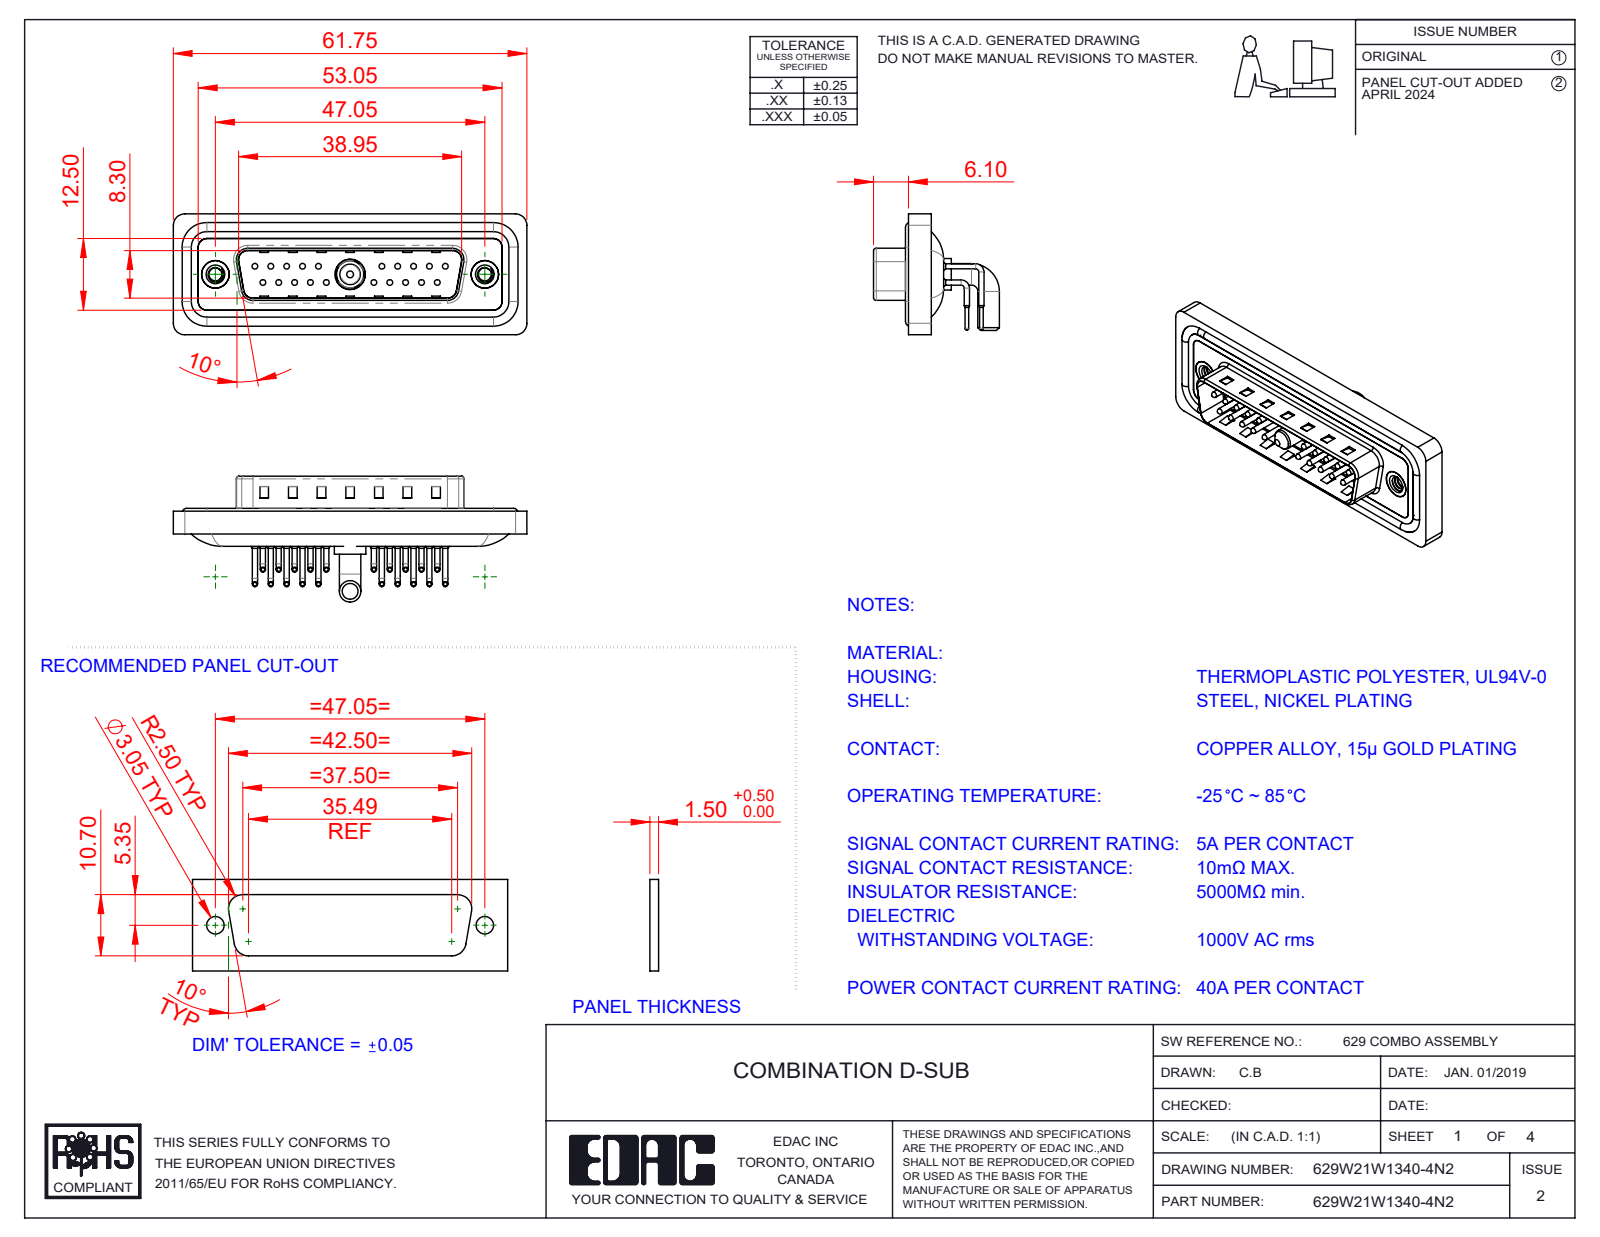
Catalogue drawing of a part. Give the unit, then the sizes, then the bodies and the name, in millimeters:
Units: millimetres
Overall size (bounding box): 61.75 × 21.98 × 21.1
Round holes (diameter × count): ⌀0.75 ×20, ⌀1.6 ×20, ⌀2 ×20, ⌀2.26 ×2, ⌀4 ×2, ⌀4.8 ×2, ⌀5 ×2, ⌀4.85 ×1, ⌀5.3 ×1
Round bosses / shafts (diameter × count): ⌀0.9 ×40, ⌀1.5 ×20, ⌀1 ×20, ⌀0.65 ×20, ⌀1.6 ×4, ⌀4.9 ×2, ⌀3.75 ×2, ⌀5.5 ×1
Partial cylindrical surfaces — rounded edges, fillets, slot ends (radius × count): R1.01 ×20, R1.5 ×18, R2 ×18, R0.5 ×8, R1.6 ×8, R0.25 ×4, R0.6 ×4, R0.65 ×4
Main face-to-face distances: 0.4, 2.9, 0.8, 4.1, 1.1, 2.1, 1.6, 4.5, 1.5, 2.5
Hole centre spacings: 3.16, 2.77, 5.54, 8.31, 5.04, 19.39, 20.97, 22.16
Volume: 7 502 mm³ · Surface area: 12 765 mm²
Bodies: 29 solids, 2726 faces (1499 planar, 929 cylindrical, 298 other)
Part name (STEP PRODUCT): 629W21W1340-4N2; 629Combo Shell Rear_25 Contacts; Power Pin_40A RA; 629Combo Contact Row 1 (+5 more)
STEP written by: SolidWorks 2023 (CONFIG_CONTROL_DESIGN)
